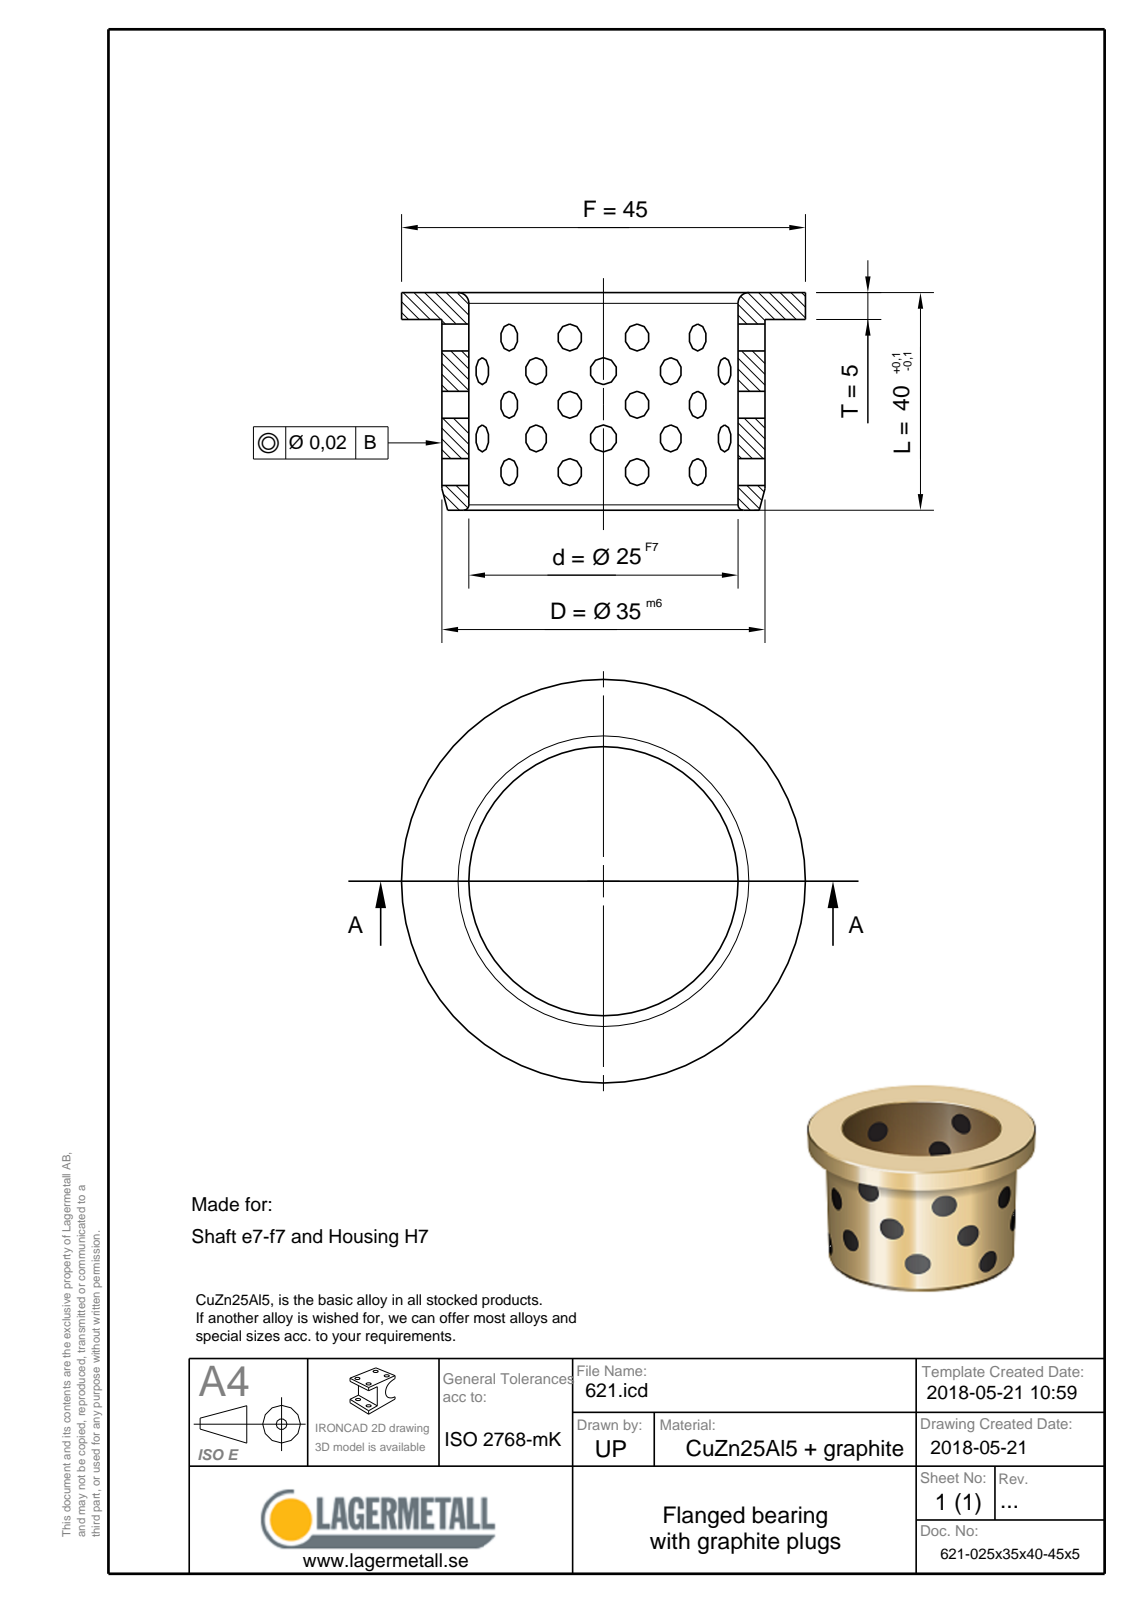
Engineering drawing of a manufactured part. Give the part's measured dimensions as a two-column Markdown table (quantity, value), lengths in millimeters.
| quantity | value |
| --- | --- |
| part name | 621-025x35x40-45x5 |
| STEP written by | Spatial InterOp 3D (CONFIG_CONTROL_DESIGN) |
| units | millimeters |
| bodies | 1 solid, 9 faces (3 planar, 3 cylindrical, 3 other) |
| overall size | 45 × 45 × 40 |
| volume | 21 815 mm³ |
| surface area | 9 701 mm² |
| round holes (diameter × count) | 25 × 1 |
| round bosses / shafts (diameter × count) | 45 × 1, 35 × 1 |
| main face-to-face distances | 5, 35, 40 |
